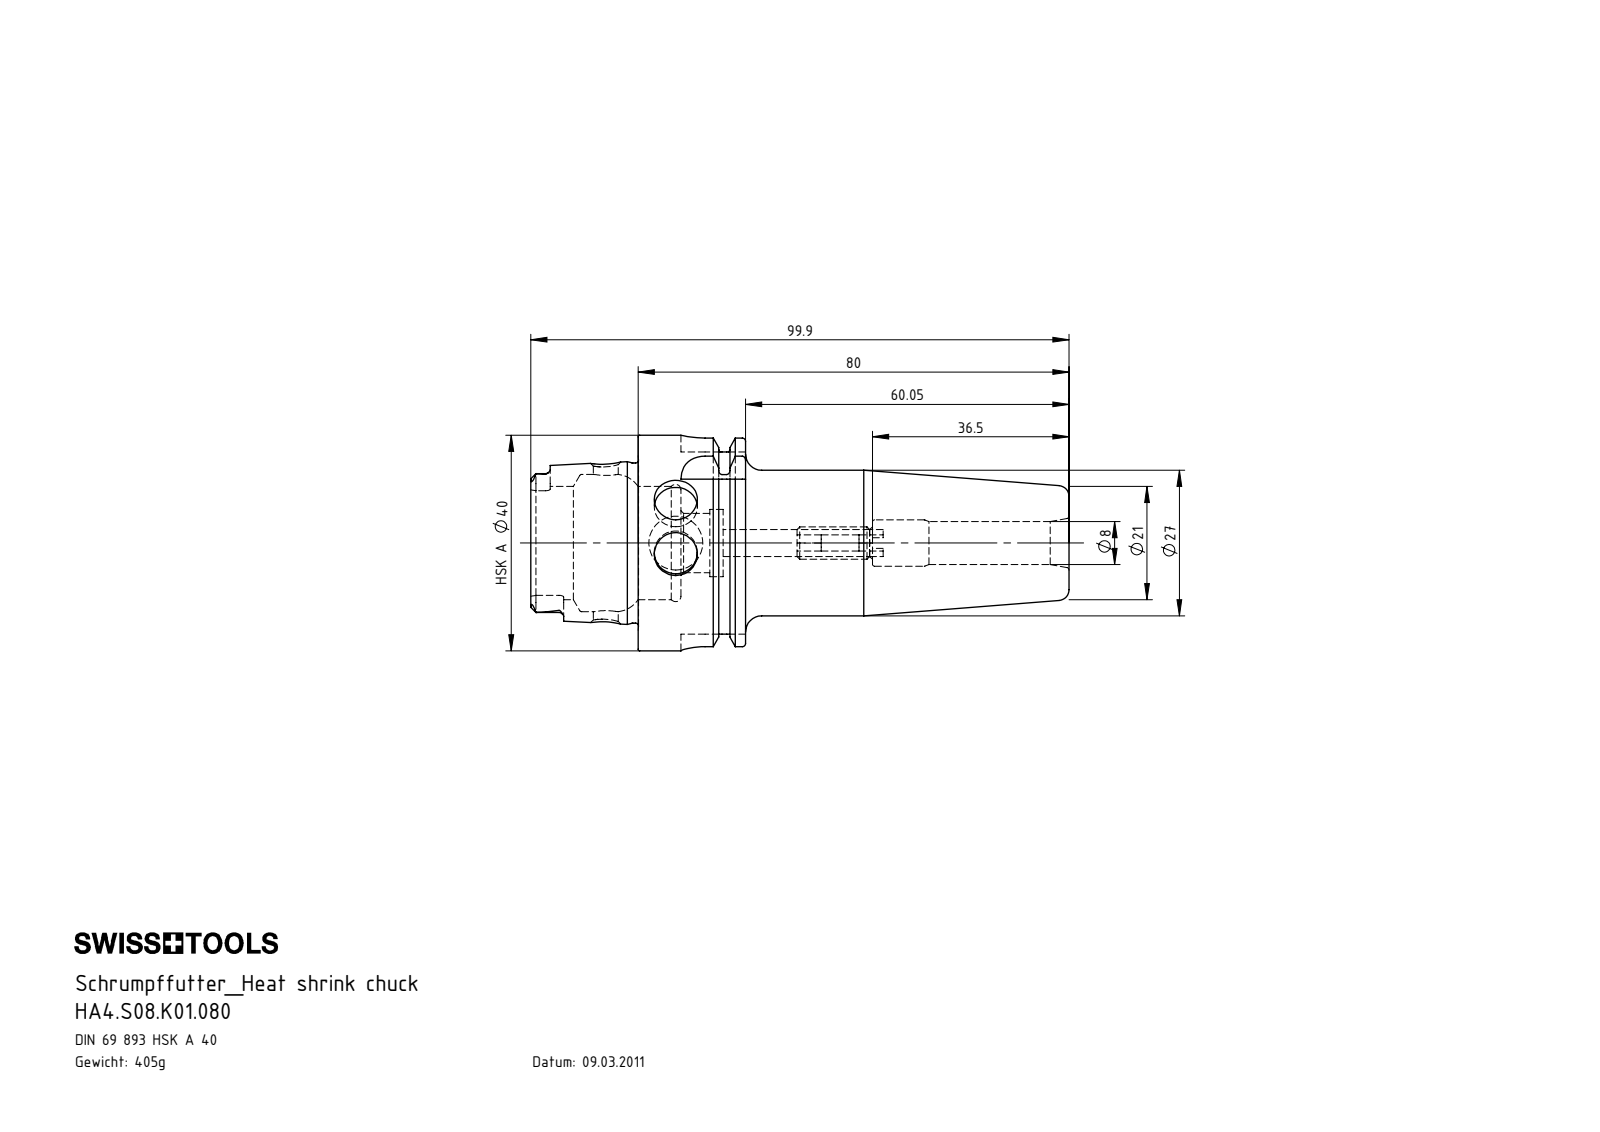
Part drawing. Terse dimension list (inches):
name: HA4.S08.K01.080; ERU-AN2.K01.016_A; HA4-S08.K01.080_C_Fertigbearbeitung
written by: SolidWorks 2017 (CONFIG_CONTROL_DESIGN)
unit: in
bodies: 2 solids, 226 faces (80 planar, 60 cylindrical, 86 other)
size: 3.933 × 1.575 × 1.575
volume: 3.15 in³; area: 24.56 in²
holes: 3× ⌀0.315, 1× ⌀0.118, 1× ⌀0.181, 1× ⌀0.197, 1× ⌀0.339, 1× ⌀0.394, 1× ⌀0.433, 1× ⌀0.492, 1× ⌀0.827, 1× ⌀1.004
bosses: 1× ⌀1.575, 1× ⌀1.368, 1× ⌀1.17, 1× ⌀1.063, 1× ⌀0.236
rounds: 6× R0.035, 4× R0.074, 4× R0.177
face distances: 0.785, 0.313, 0.472, 3.15, 2.837, 2.364, 0.783, 1.096, 1.569, 3.933
